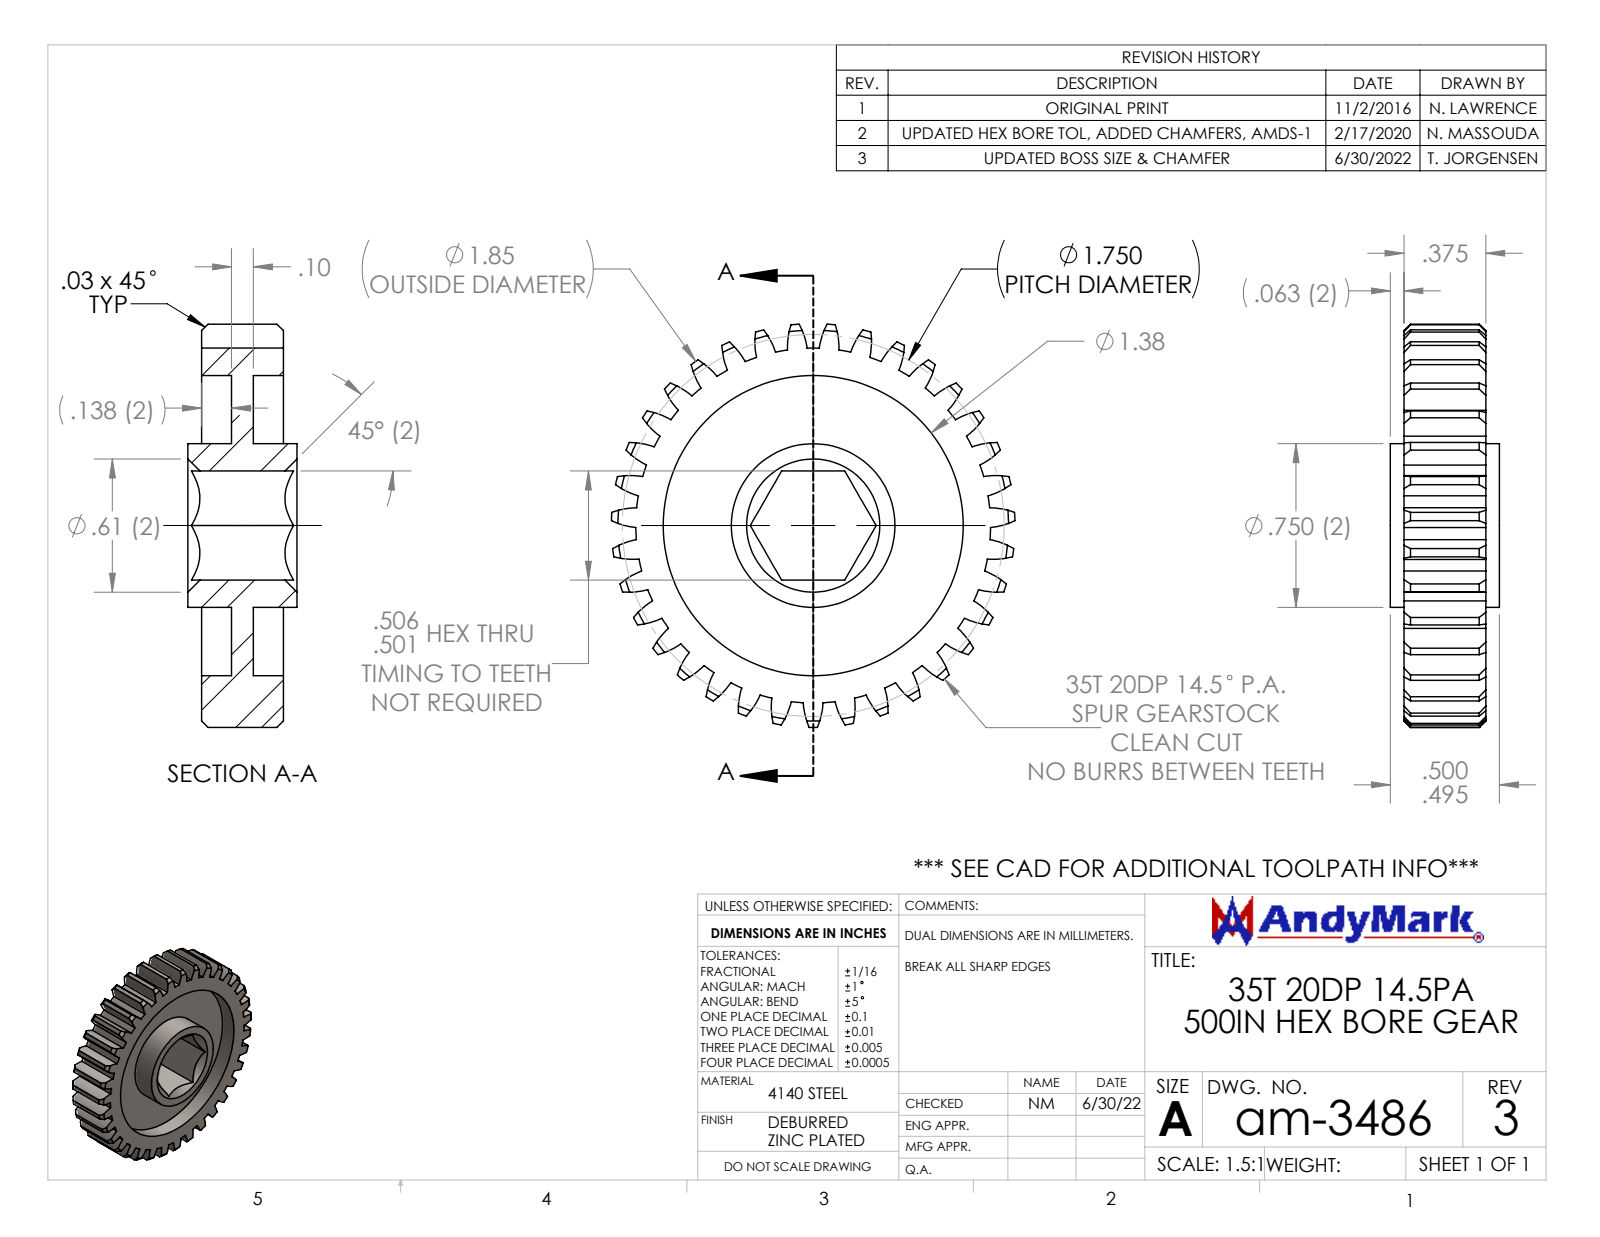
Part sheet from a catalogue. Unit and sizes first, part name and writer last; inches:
Units: inches
Overall size (bounding box): 1.849 × 1.848 × 0.5
Round holes (diameter × count): ⌀1.375 ×1
Round bosses / shafts (diameter × count): ⌀0.75 ×1
Partial cylindrical surfaces — rounded edges, fillets, slot ends (radius × count): R0.35 ×70, R0.813 ×1, R0.925 ×1
Main face-to-face distances: 0.1, 0.137, 0.237, 0.375, 0.238, 0.138, 0.5, 0.2, 0.3, 0.063
Volume: 0.539 in³ · Surface area: 11.38 in²
Bodies: 1 solid, 238 faces (12 planar, 152 cylindrical, 74 other)
Part name (STEP PRODUCT): am-3486 35T 20DP 500hex 375 FW
STEP written by: SolidWorks 2022 (CONFIG_CONTROL_DESIGN)
